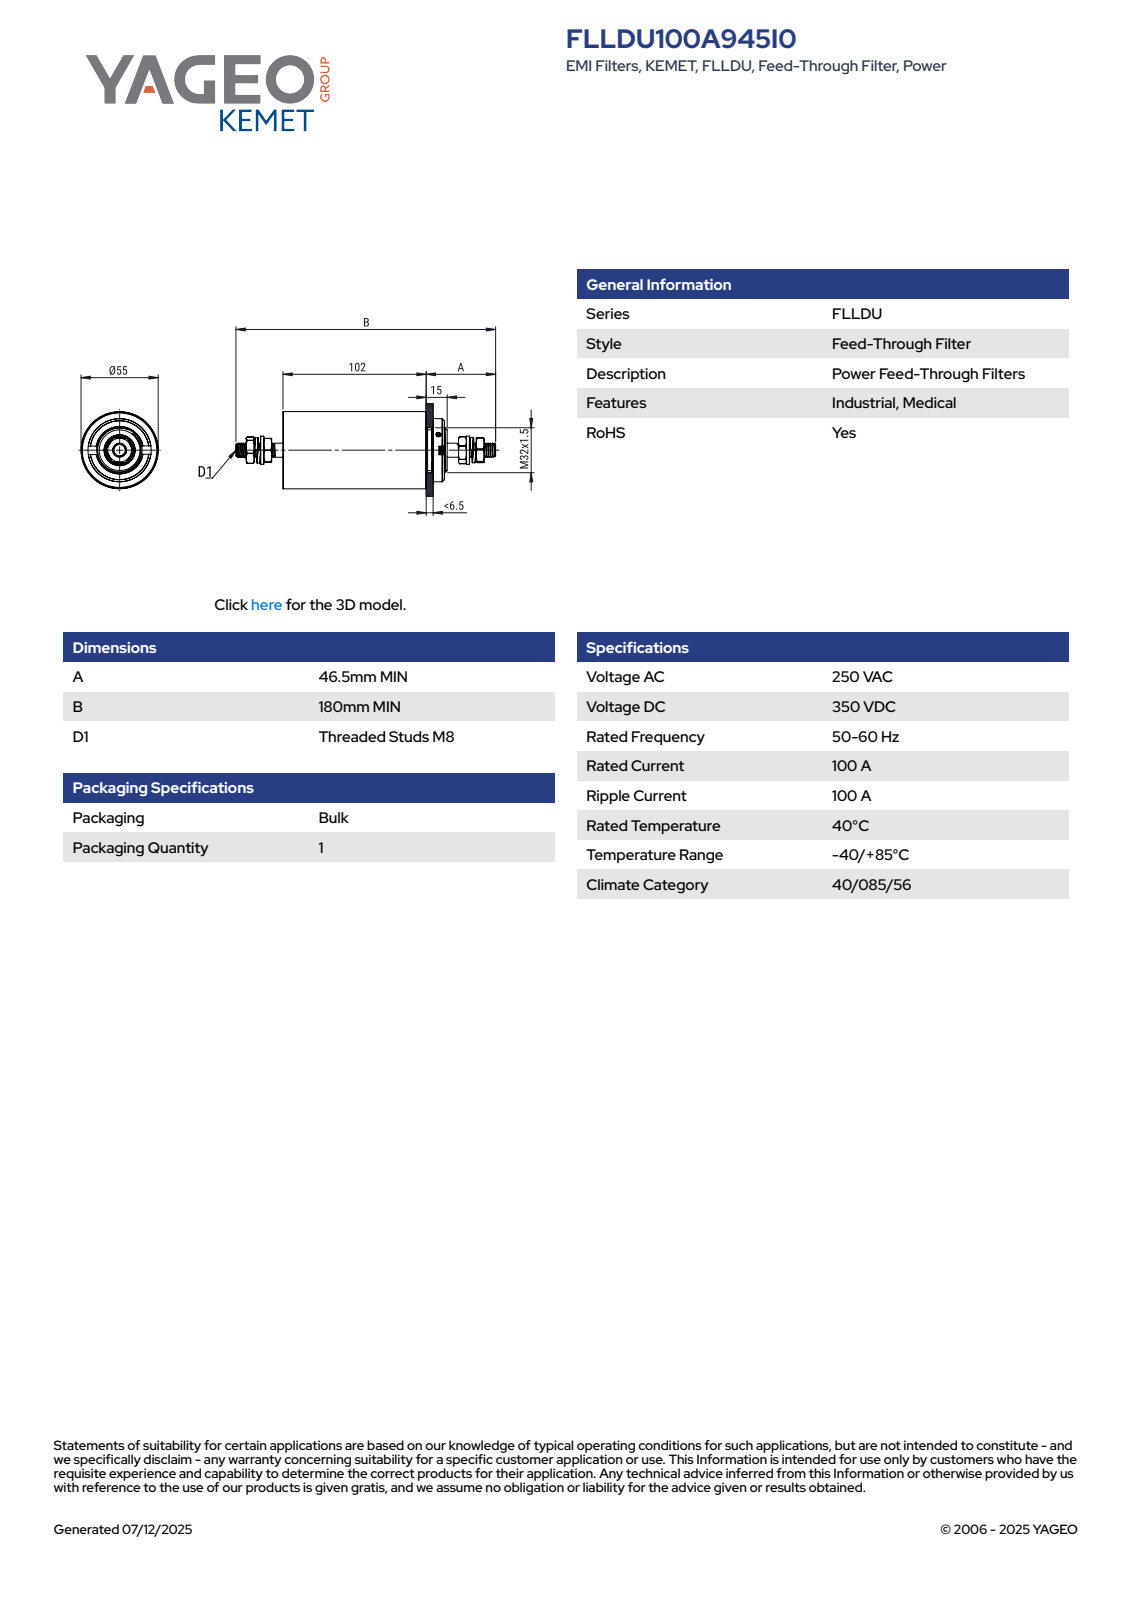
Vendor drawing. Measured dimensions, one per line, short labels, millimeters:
name: HEX NUT M8x1.25_90592A022; WASHER M8 Ø16_93475A270; GEH0026; DIC0007 (+5 more)
written by: SolidWorks 2021 (AUTOMOTIVE_DESIGN)
unit: mm
bodies: 14 solids, 450 faces (63 planar, 210 cylindrical, 177 other)
size: 180 × 55 × 55
volume: 53 801 mm³; area: 61 753 mm²
holes: 1× ⌀8.4, 1× ⌀22, 1× ⌀30.7, 1× ⌀53
bosses: 1× ⌀55, 1× ⌀54, 1× ⌀45, 1× ⌀32, 1× ⌀29, 1× ⌀22.1, 1× ⌀16, 1× ⌀8
rounds: 24× R0.2
face distances: 4, 101.5, 97.5, 13, 5, 114.5, 110.5, 102.5, 8, 106.5
